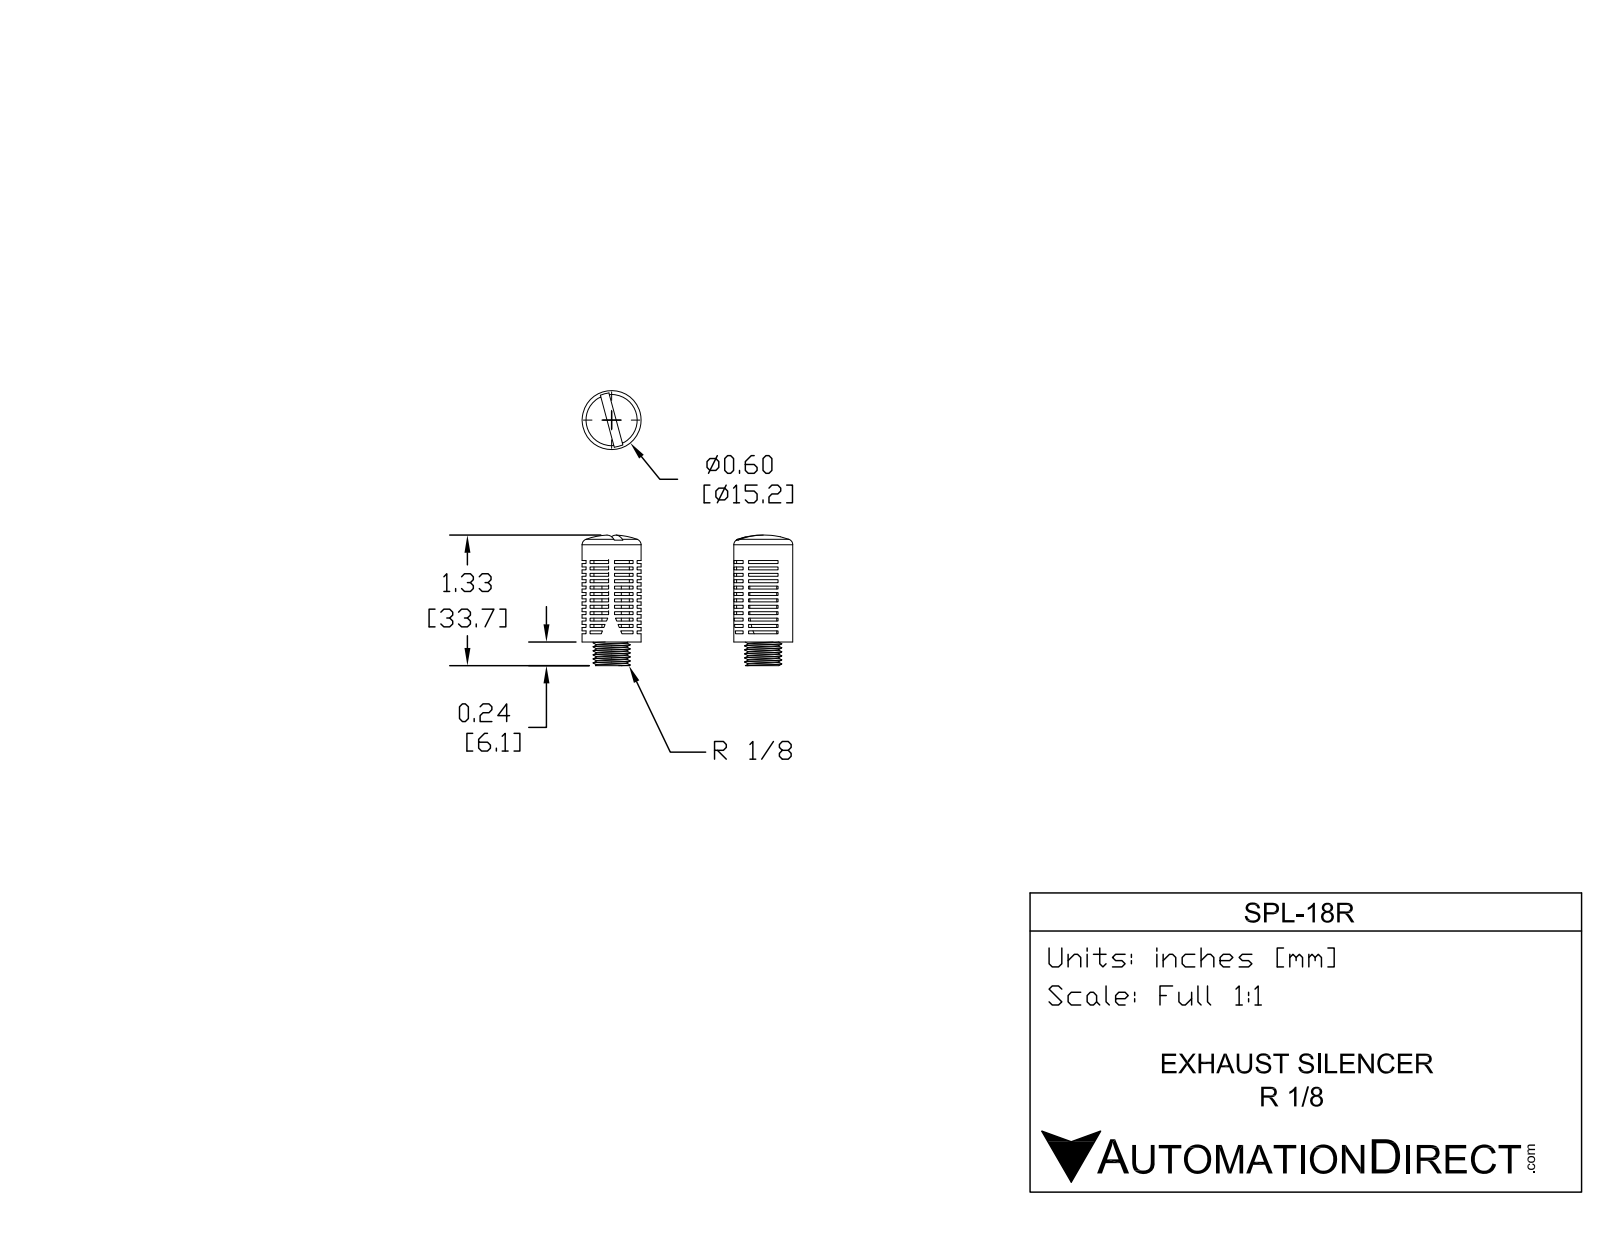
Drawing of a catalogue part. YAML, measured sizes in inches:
part_name: "SPL-18R"
step_written_by: "SolidWorks 2015 (CONFIG_CONTROL_DESIGN)"
units: inches
bodies: {solids: 1, faces: 316, planar: 287, cylindrical: 20, other: 9}
overall_size: [1.329, 0.6, 0.6]
volume: 0.099
surface_area: 6.686
round_holes:
  - {diameter: 0.28, count: 1}
  - {diameter: 0.546, count: 1}
round_bosses_or_shafts:
  - {diameter: 0.6, count: 1}
  - {diameter: 0.375, count: 1}
  - {diameter: 0.359, count: 1}
face_to_face_distances: [0.065, 0.13, 0.03, 0.1, 0.26, 0.195, 0.035, 0.13, 0.195, 0.16]
